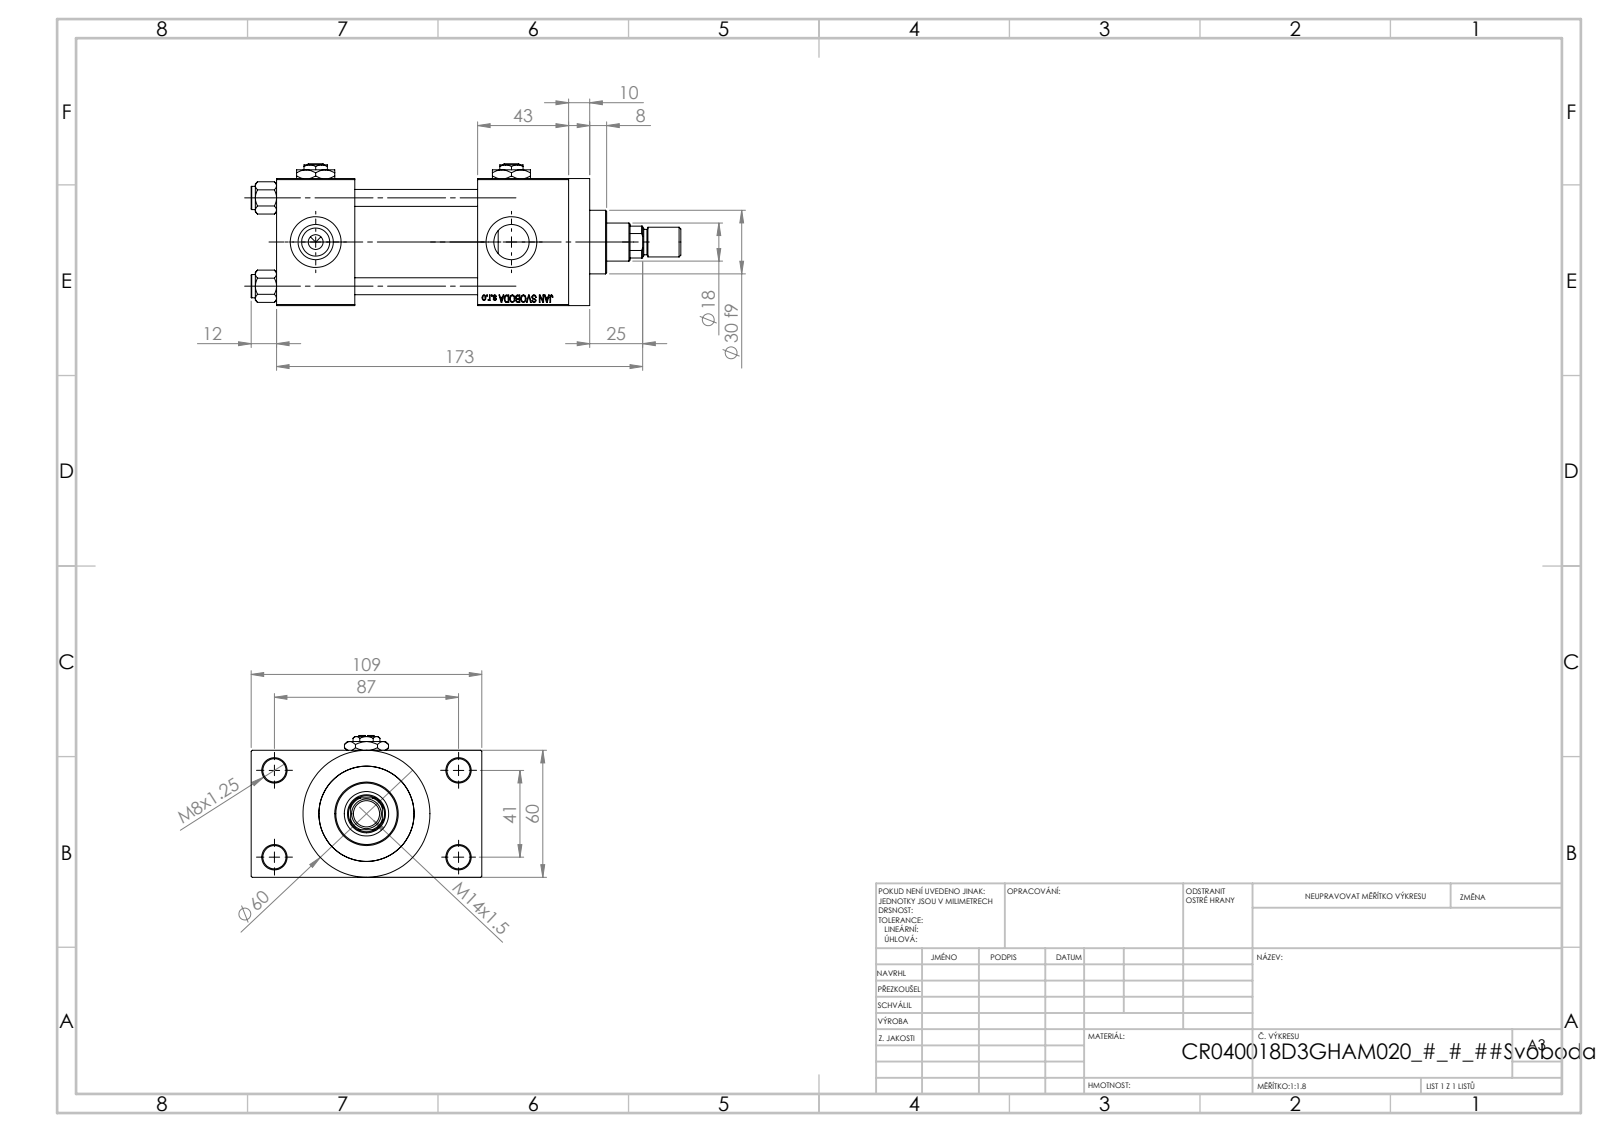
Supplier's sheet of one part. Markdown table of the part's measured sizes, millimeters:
| quantity | value |
| --- | --- |
| part name | V215CR_D_Body; ROD_END_AH; V215_VC_A; V215CR_VCP_D (+3 more) |
| STEP written by | SolidWorks 2019 (CONFIG_CONTROL_DESIGN) |
| units | millimeters |
| bodies | 14 solids, 1219 faces (550 planar, 103 cylindrical, 566 other) |
| overall size | 203 × 109 × 67 |
| volume | 513 009 mm³ |
| surface area | 126 318 mm² |
| round holes (diameter × count) | 8 × 4, 11 × 4, 16.66 × 4, 24 × 4, 7 × 3, 8.5 × 1, 18 × 1, 21 × 1, 31 × 1, 40 × 1, 45 × 1 |
| round bosses / shafts (diameter × count) | 11 × 4, 60 × 1, 46 × 1, 30 × 1, 14 × 1, 12 × 1 |
| partial cylindrical surfaces (radius × count) | 8.5 × 1 |
| main face-to-face distances | 60, 58, 24.5, 84.5, 37, 95, 43, 138, 101, 53 |
| hole center spacings | 22.65, 29.49, 41.7, 47.15, 48.09, 64.35, 76.49, 41 |
